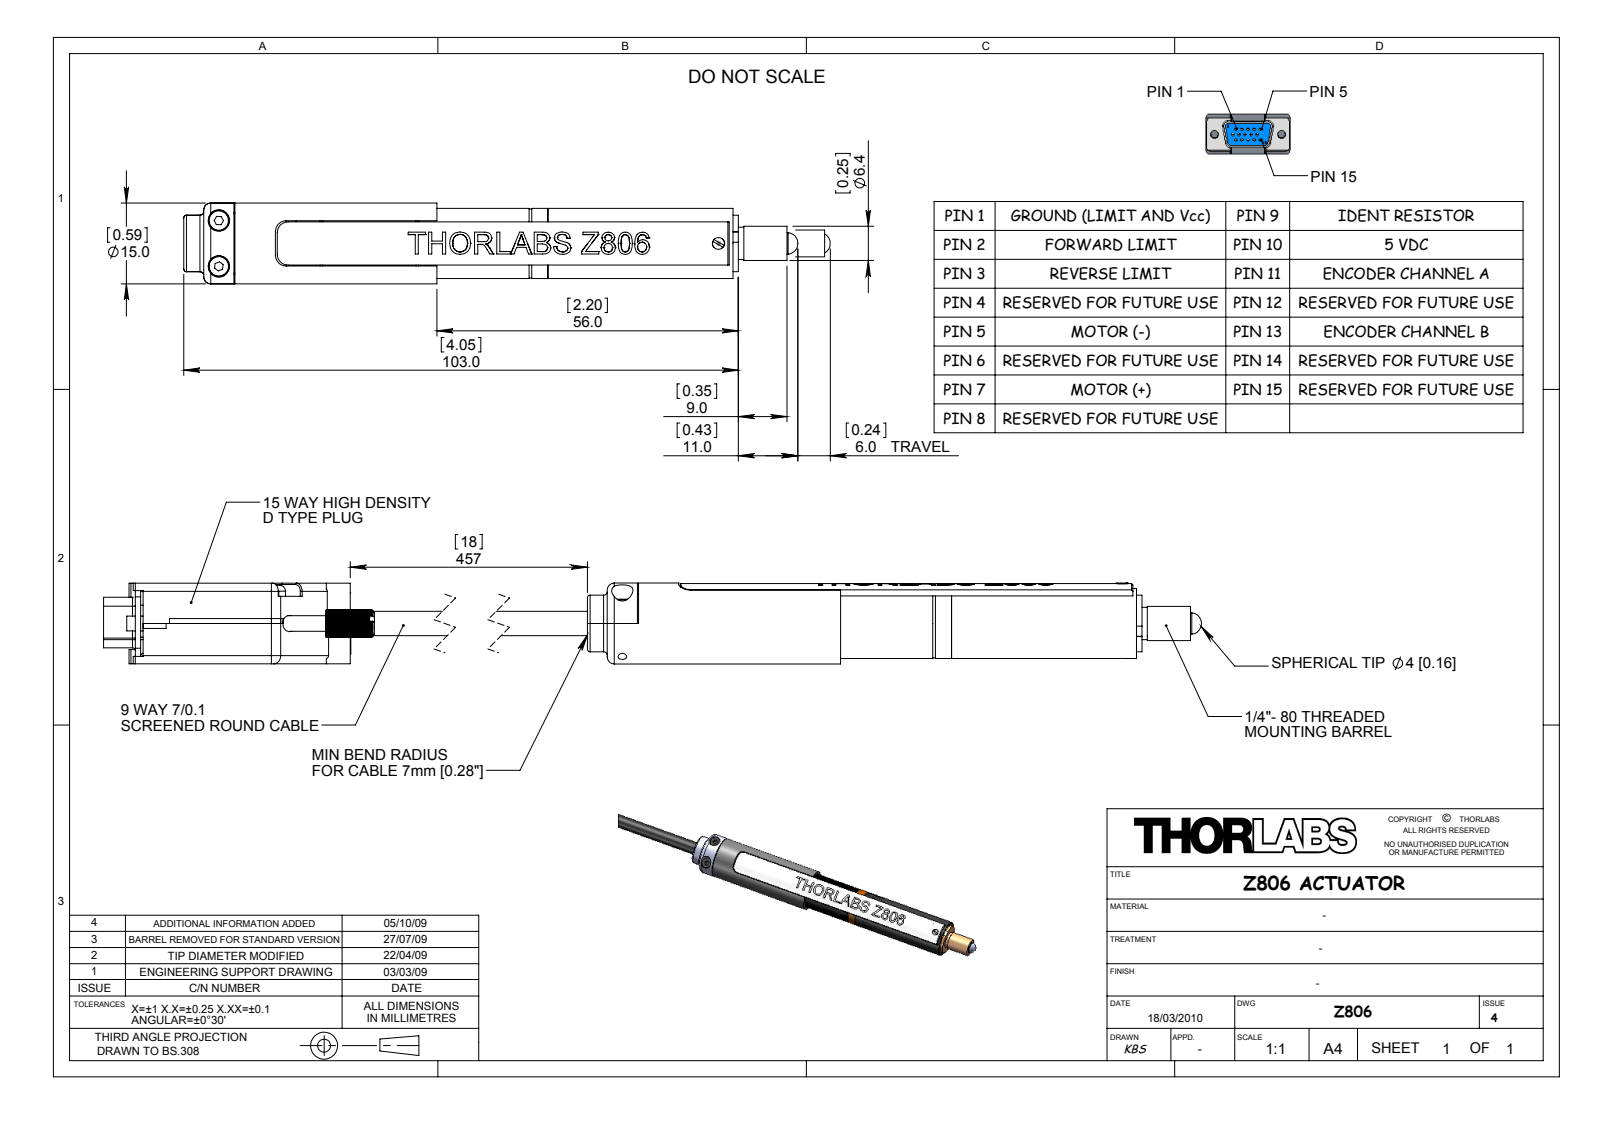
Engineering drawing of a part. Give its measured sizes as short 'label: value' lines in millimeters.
name: 17630-E0W; Hi D Conn with round cable; BA0701; BB0692 9 Way D Type Shell (+8 more)
written by: SolidWorks 2011 (AUTOMOTIVE_DESIGN)
unit: mm
bodies: 26 solids, 2003 faces (1044 planar, 689 cylindrical, 270 other)
size: 624.03 × 31 × 15
volume: 29 919 mm³; area: 33 764 mm²
holes: 15× ⌀1.02, 4× ⌀1.6, 4× ⌀2.1, 4× ⌀3.05, 3× ⌀0.95, 2× ⌀1.2, 2× ⌀2.26, 2× ⌀2.7, 2× ⌀3.43, 2× ⌀4, 1× ⌀1.3, 1× ⌀1.5
bosses: 15× ⌀1.52, 15× ⌀0.99, 2× ⌀5.56, 2× ⌀3.77, 2× ⌀2.89, 2× ⌀2.84, 2× ⌀2.73, 2× ⌀0.8
rounds: 24× R0.25, 19× R0.5, 14× R0.51, 12× R0.17, 12× R0.38, 12× R1.52, 10× R2.03, 8× R1
face distances: 1.39, 13.59, 7.49, 6.1, 12.2, 14.98, 1.04, 0.35, 14.63, 7.14
hole spacings: 2.28, 3.96, 4.57, 2.29, 6.05, 6.04, 8.24, 6.86
